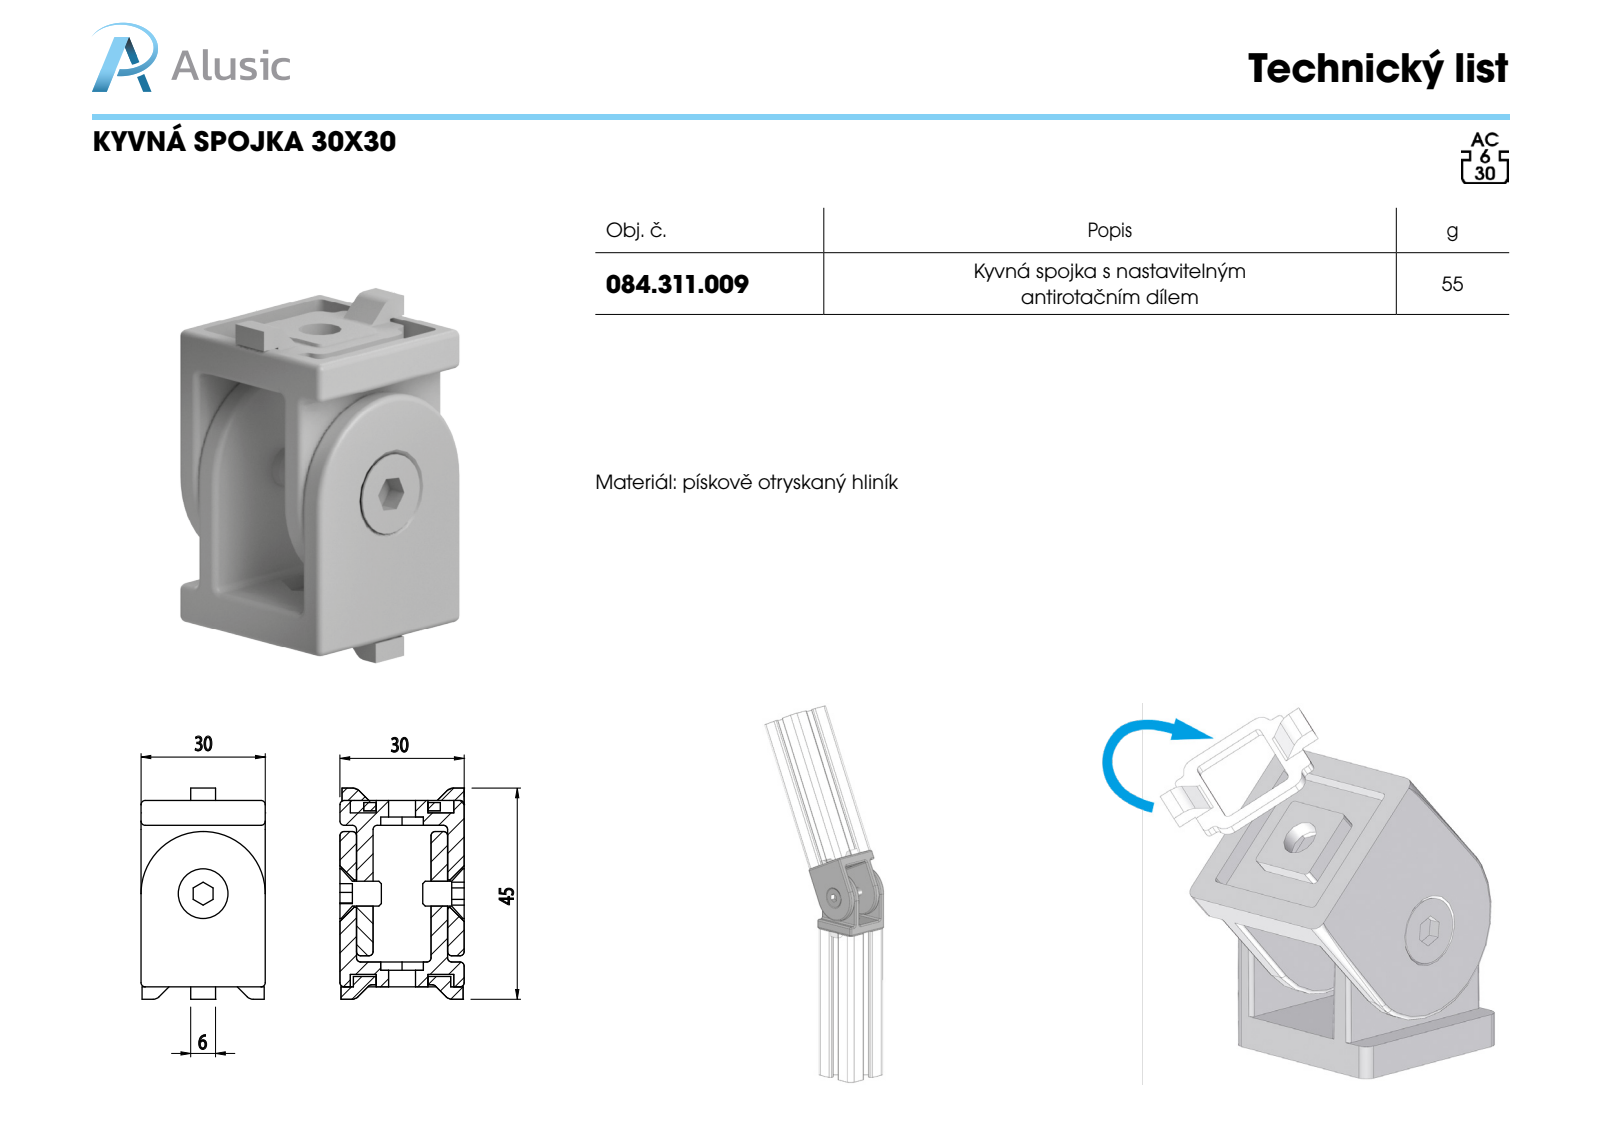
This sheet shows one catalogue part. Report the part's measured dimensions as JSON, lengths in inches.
{"part_name": "084.311.009; 084.311.009-2; 084.311.009-1", "step_written_by": "SolidWorks 2011 (CONFIG_CONTROL_DESIGN)", "units": "inches", "bodies": {"solids": 4, "faces": 270, "planar": 106, "cylindrical": 120, "other": 44}, "overall_size": [2.009, 1.187, 1.181], "volume_in3": 1.305, "surface_area_in2": 23.34, "round_holes": [[0.256, 2], [0.197, 1], [0.26, 1]], "round_bosses_or_shafts": [[1.181, 1]], "partial_cylinders_radius": [[0.039, 76], [0.079, 12]], "face_to_face_distances": [0.157, 0.866, 1.024, 0.118, 0.709, 0.315, 0.098, 1.181, 0.02, 0.217]}
